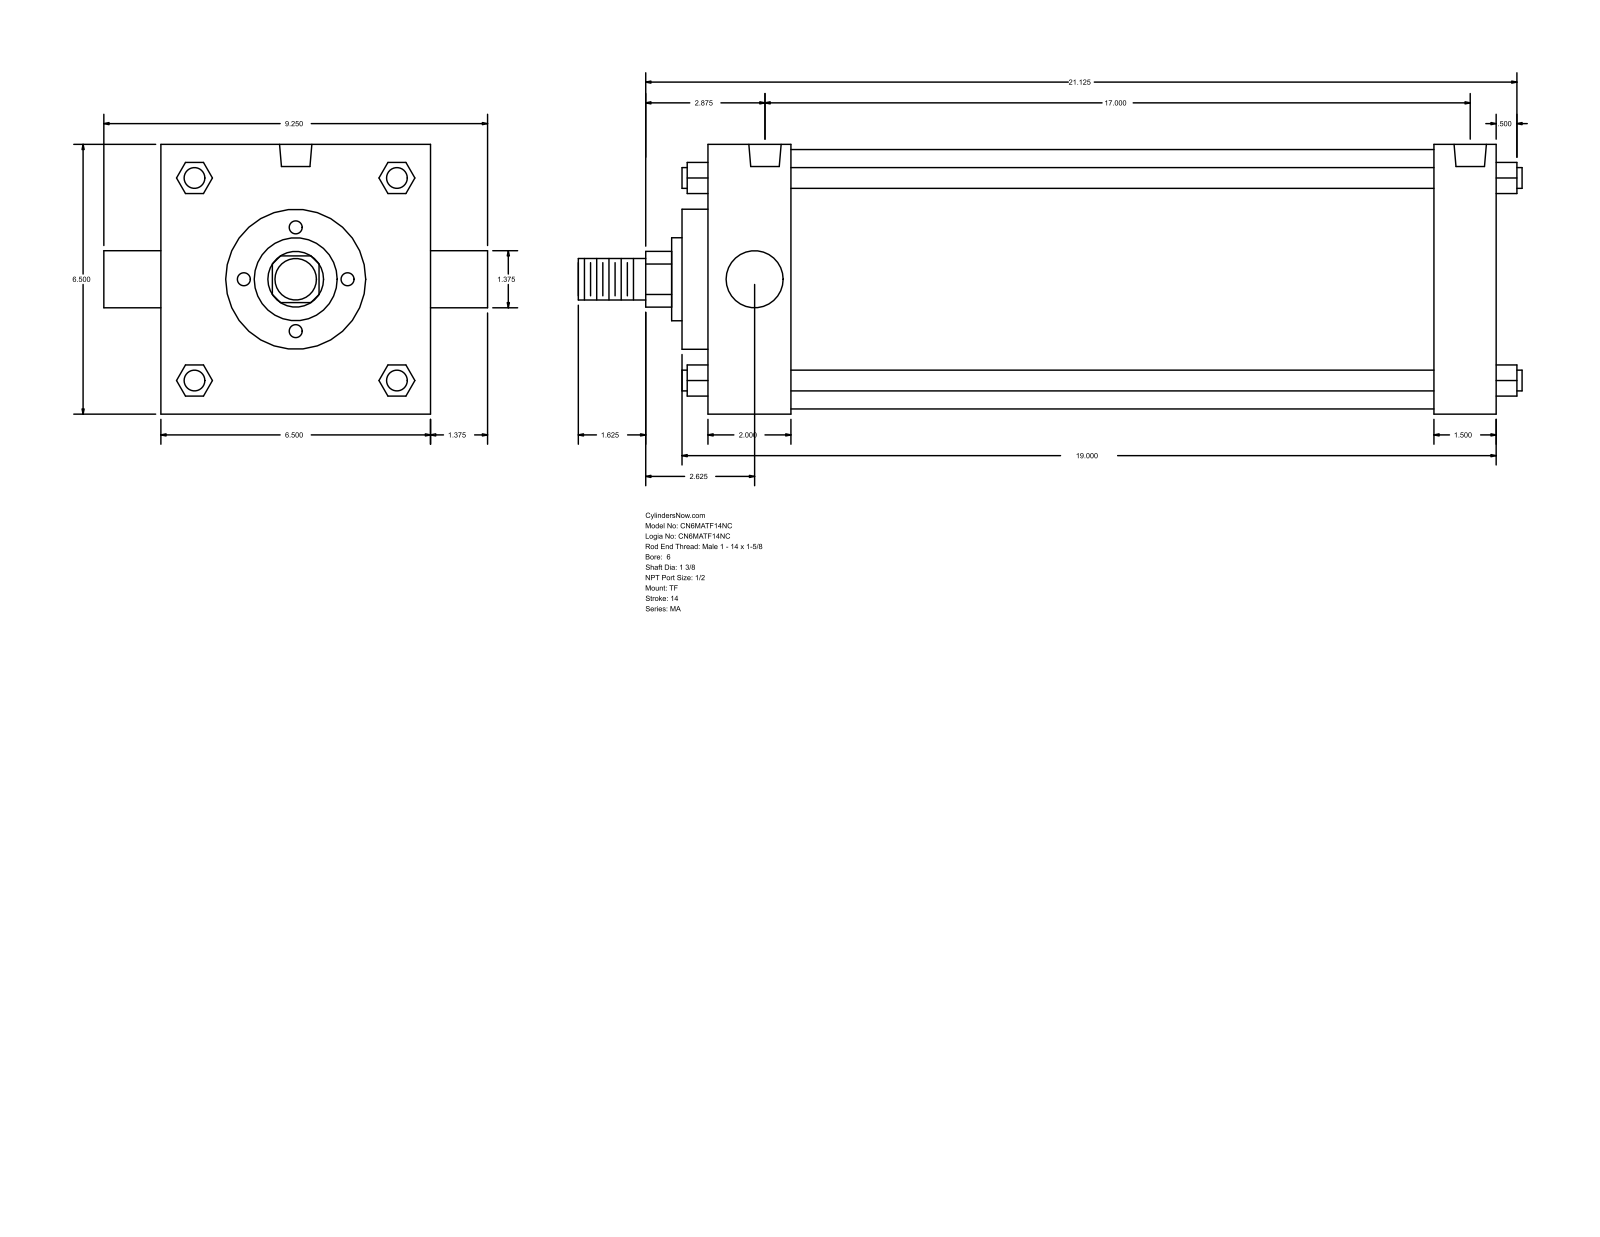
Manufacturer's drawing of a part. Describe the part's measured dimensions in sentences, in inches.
The part is named "MA_TF__0600_1.375". Its 3-D file was written by "GSSL Pune (CONFIG_CONTROL_DESIGN)". It is 0 solids with 122 faces: 93 planar, 29 cylindrical and 0 other. Overall it measures 22.75 by 9.25 by 6.5 inches. Round holes: 3 of diameter 0.687, 2 of diameter 0.778. Round bosses or shafts: 4 of diameter 0.5, 2 of diameter 1.375, 1 of diameter 6.25, 1 of diameter 3.375, 1 of diameter 2, 1 of diameter 1. Partial cylindrical surfaces (rounded edges, fillets, slot ends): 1 of radius 0.672. The main face-to-face distances are 6.5, 19.125, 2, 17.125, 17.625, 15.625, 1.5, 2.625, 0.625, 18.25. The hole center spacings are 0.125, 17, 17.125.
